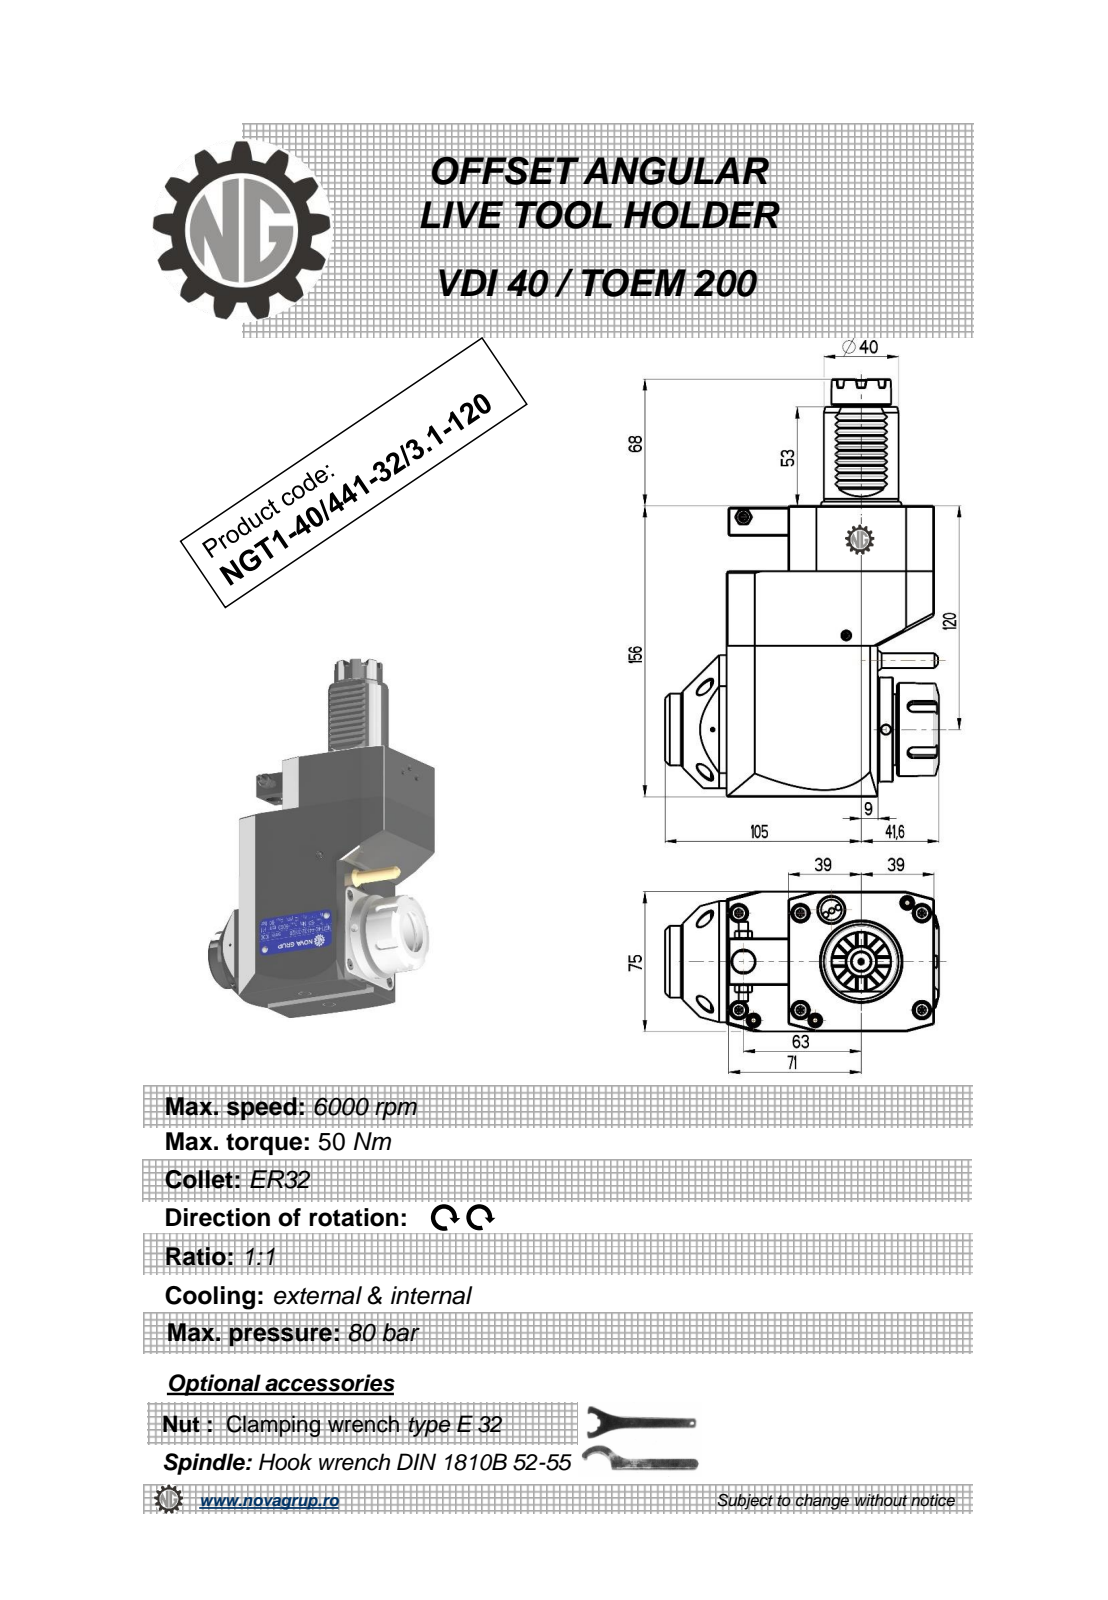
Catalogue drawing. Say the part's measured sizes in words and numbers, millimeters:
The part is named "NGT1_40_441_32_3_1_120". Its 3-D file was written by "PRO/ENGINEER BY PARAMETRIC TECHNOLOGY CORPORATION, 2010280 (CONFIG_CONTROL_DESIGN)". It is 1 solid with 501 faces: 242 planar, 83 cylindrical and 176 other. Overall it measures 224 by 146.6 by 75 millimeters. Its volume is 1 220 000 cubic millimeters and its surface area 91 338 square millimeters. Round holes: 3 of diameter 5, 1 of diameter 3, 1 of diameter 9.5, 1 of diameter 12, 1 of diameter 27. Round bosses or shafts: 1 of diameter 56, 1 of diameter 50, 1 of diameter 43, 1 of diameter 40, 1 of diameter 38.5, 1 of diameter 32, 1 of diameter 17.2, 1 of diameter 10. Partial cylindrical surfaces (rounded edges, fillets, slot ends): 12 of radius 0.26, 10 of radius 0.3, 6 of radius 0.2, 5 of radius 3, 1 of radius 0.5, 1 of radius 40. The main face-to-face distances are 75, 156, 111, 33, 35, 121, 81, 30, 78, 48. The hole center spacings are 40.93, 76.25, 77.5, 112.5.
